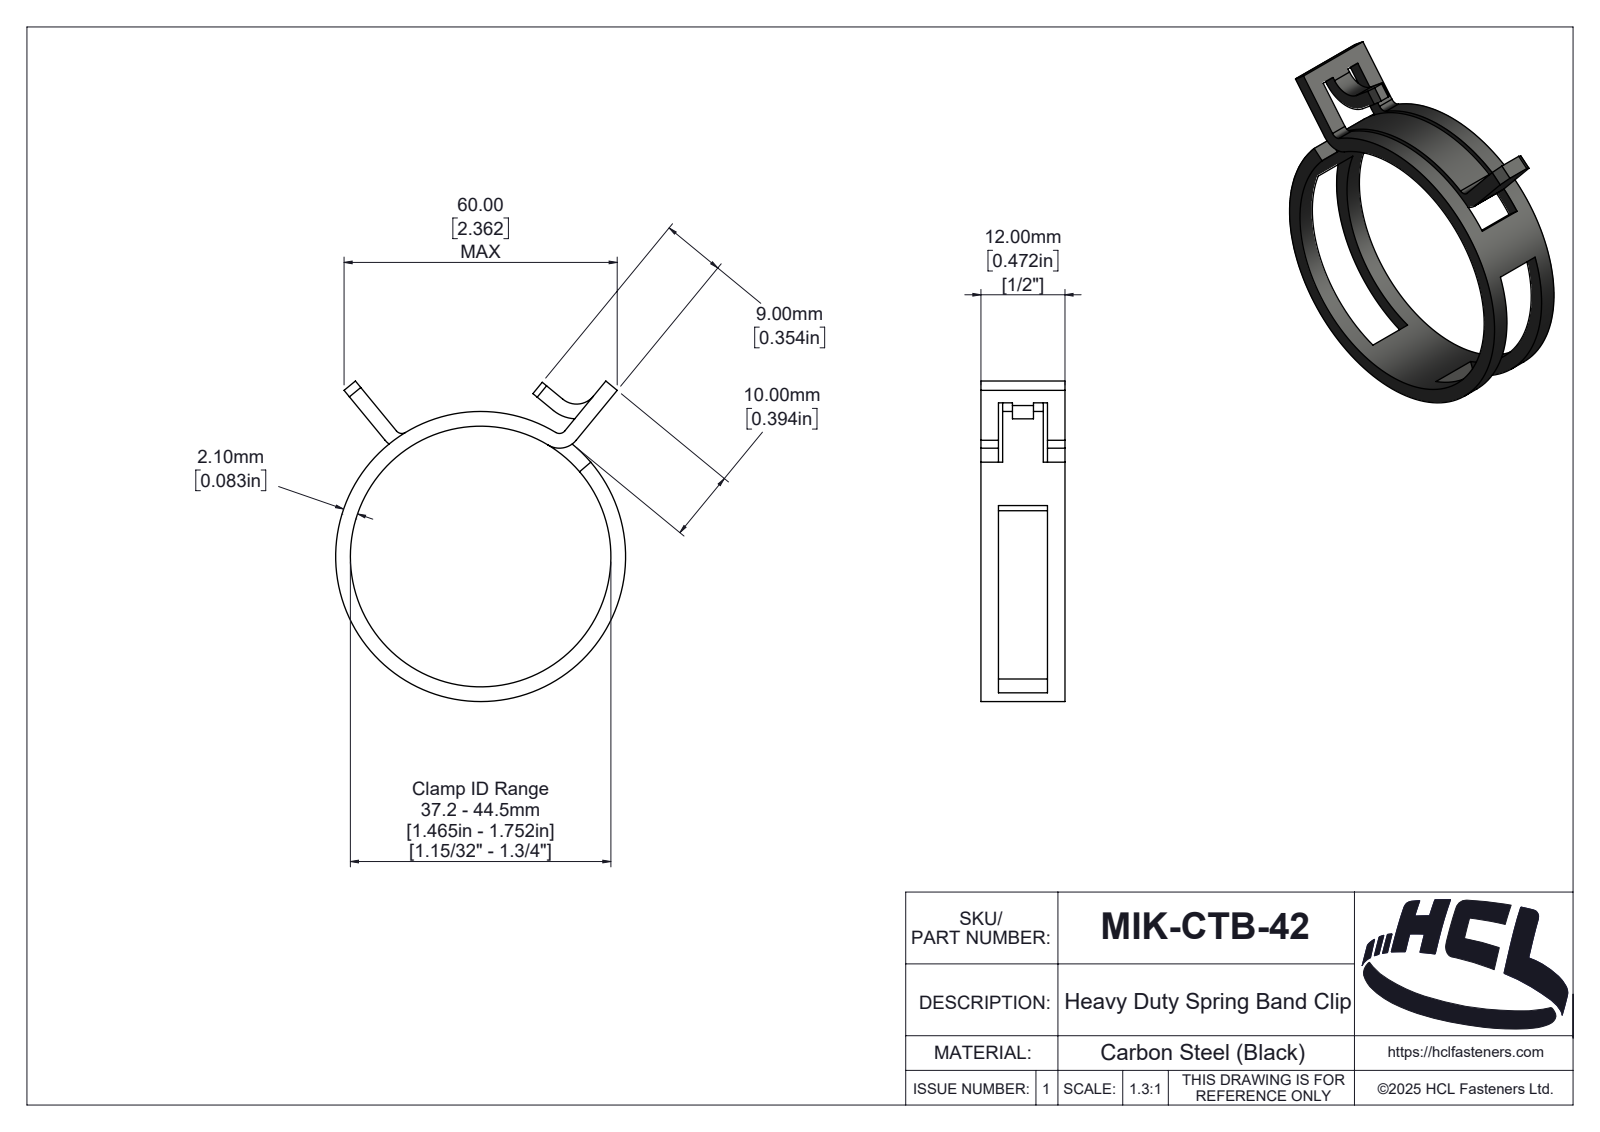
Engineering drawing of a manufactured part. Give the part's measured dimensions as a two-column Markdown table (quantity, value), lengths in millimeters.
| quantity | value |
| --- | --- |
| part name | MIK-CTB-42 |
| STEP written by | SolidWorks 2025 (AUTOMOTIVE_DESIGN) |
| units | millimeters |
| bodies | 1 solid, 149 faces (36 planar, 64 cylindrical, 49 other) |
| overall size | 45.74 × 41.4 × 12 |
| volume | 2 343 mm³ |
| surface area | 3 547 mm² |
| round holes (diameter × count) | 37.2 × 1 |
| round bosses / shafts (diameter × count) | 41.4 × 1 |
| partial cylindrical surfaces (radius × count) | 3.1 × 3, 1 × 2, 0.33 × 1, 1.35 × 1, 1.68 × 1, 1.77 × 1, 2.14 × 1, 3.02 × 1 |
| main face-to-face distances | 2.5, 9.5, 12, 7, 3.1, 8.9, 0.6, 6.4, 2.1, 5.8 |
